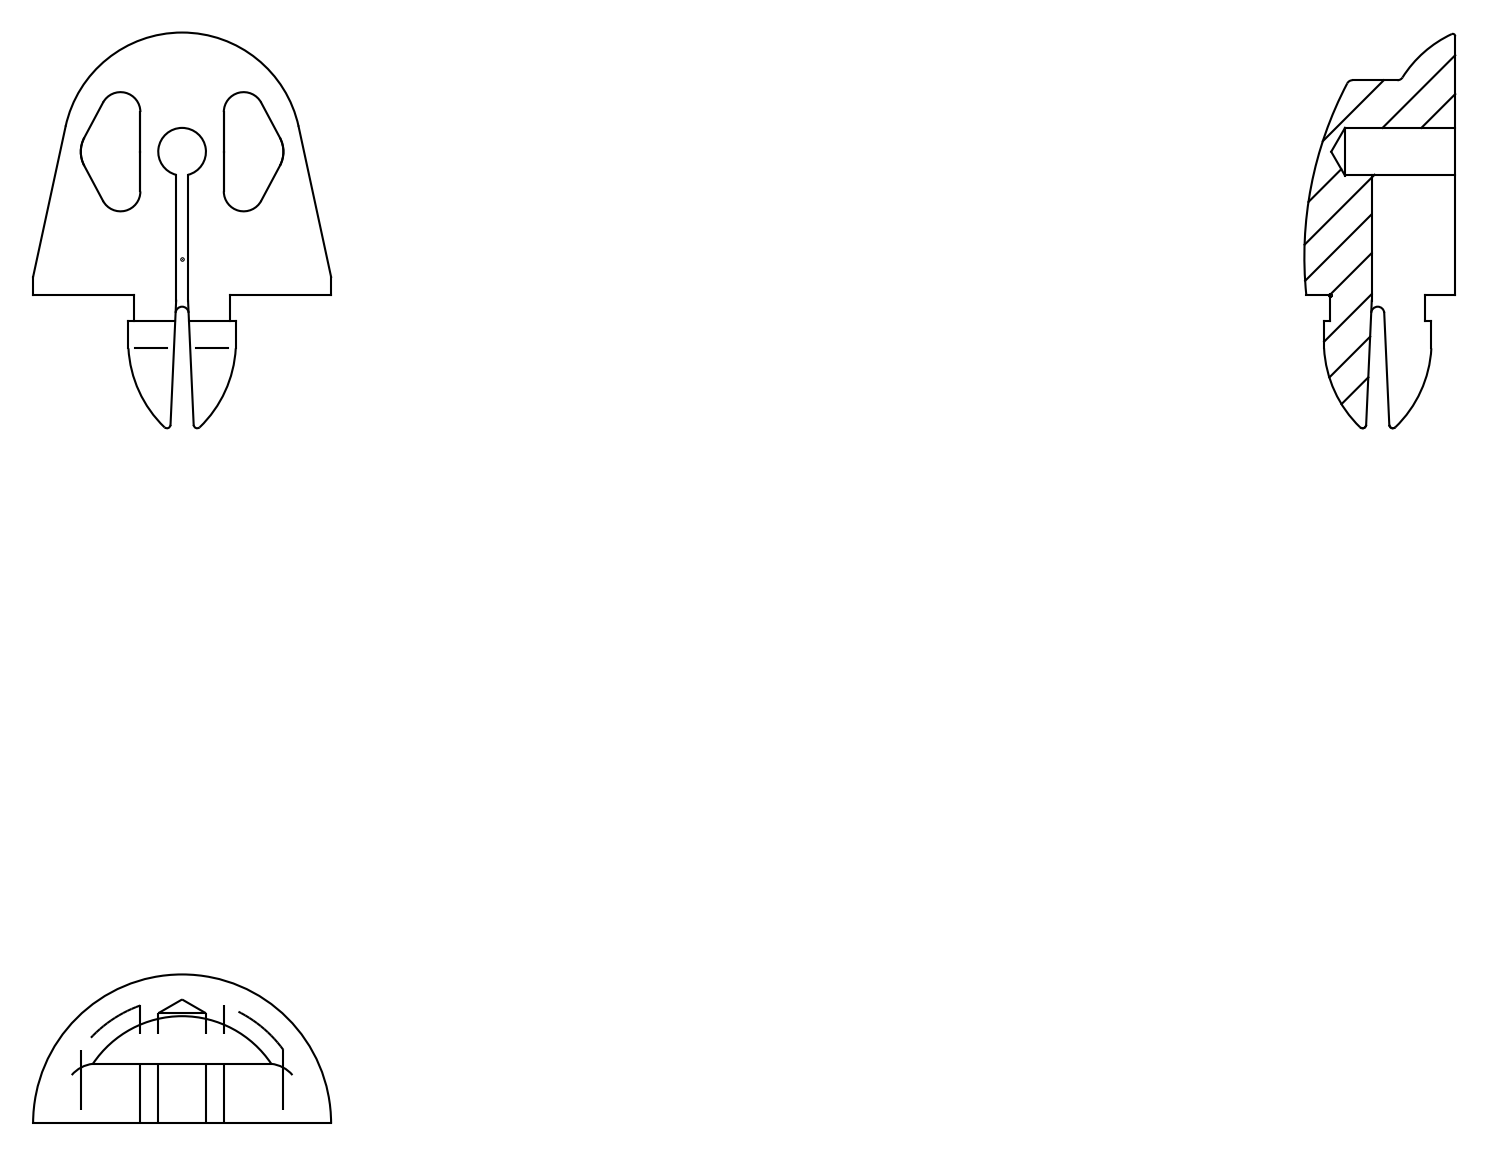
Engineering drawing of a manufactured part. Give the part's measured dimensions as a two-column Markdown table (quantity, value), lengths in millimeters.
| quantity | value |
| --- | --- |
| STEP written by | THINKDESIGN (CONFIG_CONTROL_DESIGN) |
| units | millimeters |
| bodies | 1 solid, 54 faces (28 planar, 19 cylindrical, 7 other) |
| overall size | 33.14 × 25 × 16.27 |
| volume | 3 464 mm³ |
| surface area | 2 189 mm² |
| round holes (diameter × count) | 4 × 1 |
| round bosses / shafts (diameter × count) | 9 × 1, 8 × 1 |
| partial cylindrical surfaces (radius × count) | 1.67 × 4, 0.55 × 2, 2.5 × 2, 0.8 × 1, 9.79 × 1 |
| main face-to-face distances | 1, 3, 4, 3.91, 15.58, 7, 20.2, 8.98, 29.18 |
